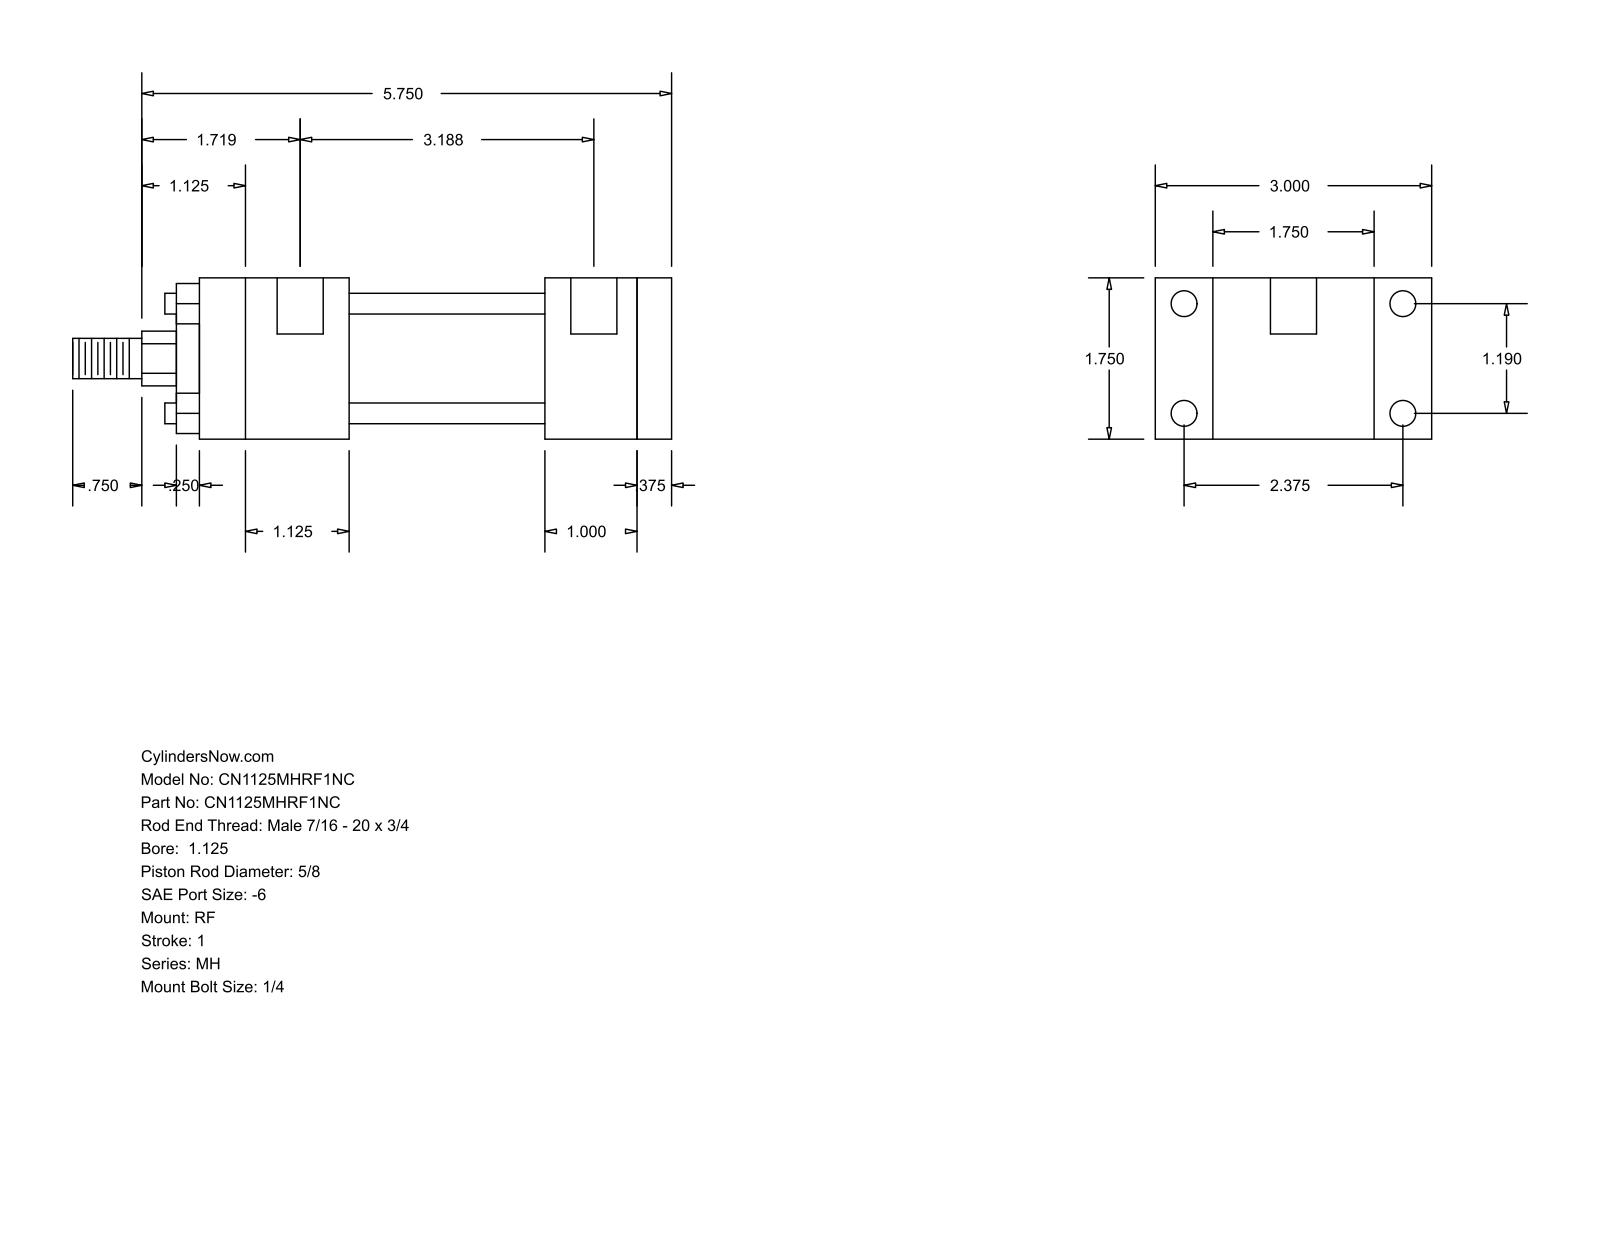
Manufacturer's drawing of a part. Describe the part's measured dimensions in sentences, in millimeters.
The part is named "MH_RF__0112_0.625". Its 3-D file was written by "GSSL Pune (CONFIG_CONTROL_DESIGN)". It is 0 solids with 92 faces: 64 planar, 28 cylindrical and 0 other. Overall it measures 165.1 by 76.2 by 44.45 millimeters. Round holes: 4 of diameter 5.56, 4 of diameter 7.14, 2 of diameter 12.7. Round bosses or shafts: 4 of diameter 5.71, 1 of diameter 34.92, 1 of diameter 28.57, 1 of diameter 15.88, 1 of diameter 11.11. Partial cylindrical surfaces (rounded edges, fillets, slot ends): 1 of radius 7.54. The main face-to-face distances are 44.46, 9.52, 34.93, 130.17, 15.87, 79.38, 88.9, 53.97, 25.41, 41.27. The hole center spacings are 30.22, 60.32, 67.47, 77.79, 3.17, 80.96.
